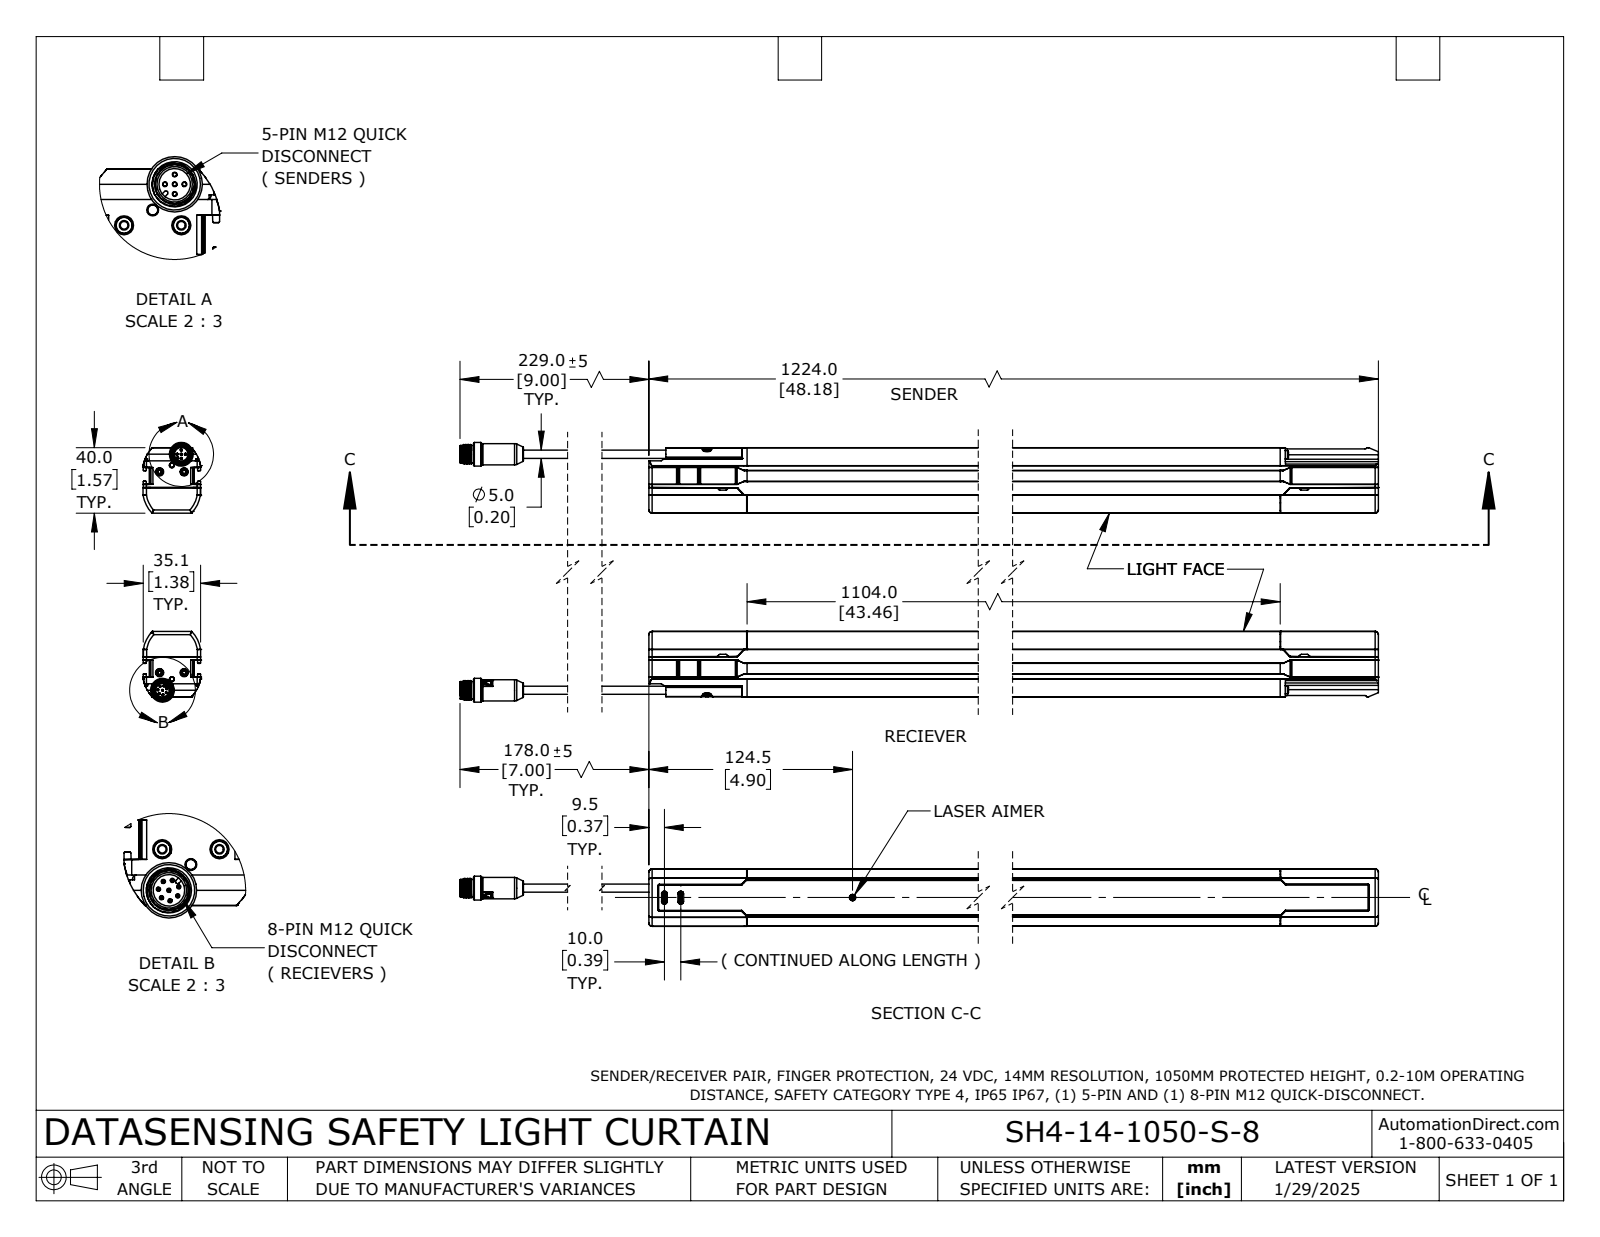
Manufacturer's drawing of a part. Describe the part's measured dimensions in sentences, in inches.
The part is named "957920062". Its 3-D file was written by "SolidWorks 2024 (AUTOMOTIVE_DESIGN)". It is 4 solids with 2600 faces: 1178 planar, 784 cylindrical and 638 other. Overall it measures 50.681 by 6.248 by 1.384 inches. Its volume is 152.2 cubic inches and its surface area 673.9 square inches. Round holes: 4 of diameter 0.079, 4 of diameter 0.118, 4 of diameter 0.197, 2 of diameter 0.1, 2 of diameter 0.101, 2 of diameter 0.102, 2 of diameter 0.102, 2 of diameter 0.325, 2 of diameter 0.382, 2 of diameter 0.407, 2 of diameter 0.425, 1 of diameter 0.11. Round bosses or shafts: 10 of diameter 0.197, 8 of diameter 0.087, 8 of diameter 0.031, 5 of diameter 0.039, 4 of diameter 0.172, 2 of diameter 0.571, 2 of diameter 0.512, 2 of diameter 0.417. Partial cylindrical surfaces (rounded edges, fillets, slot ends): 164 of radius 0.01, 66 of radius 0.016, 50 of radius 0.02, 36 of radius 0.008, 20 of radius 0.031, 12 of radius 0.031, 12 of radius 0.079, 10 of radius 0.059. The main face-to-face distances are 1.496, 4.496, 0.156, 1.222, 3, 1.378, 5.992, 1.067, 4.634, 1.033. The hole center spacings are 0.866, 5.322, 5.392, 0.429, 0.591, 0.672, 4.831, 4.867.
